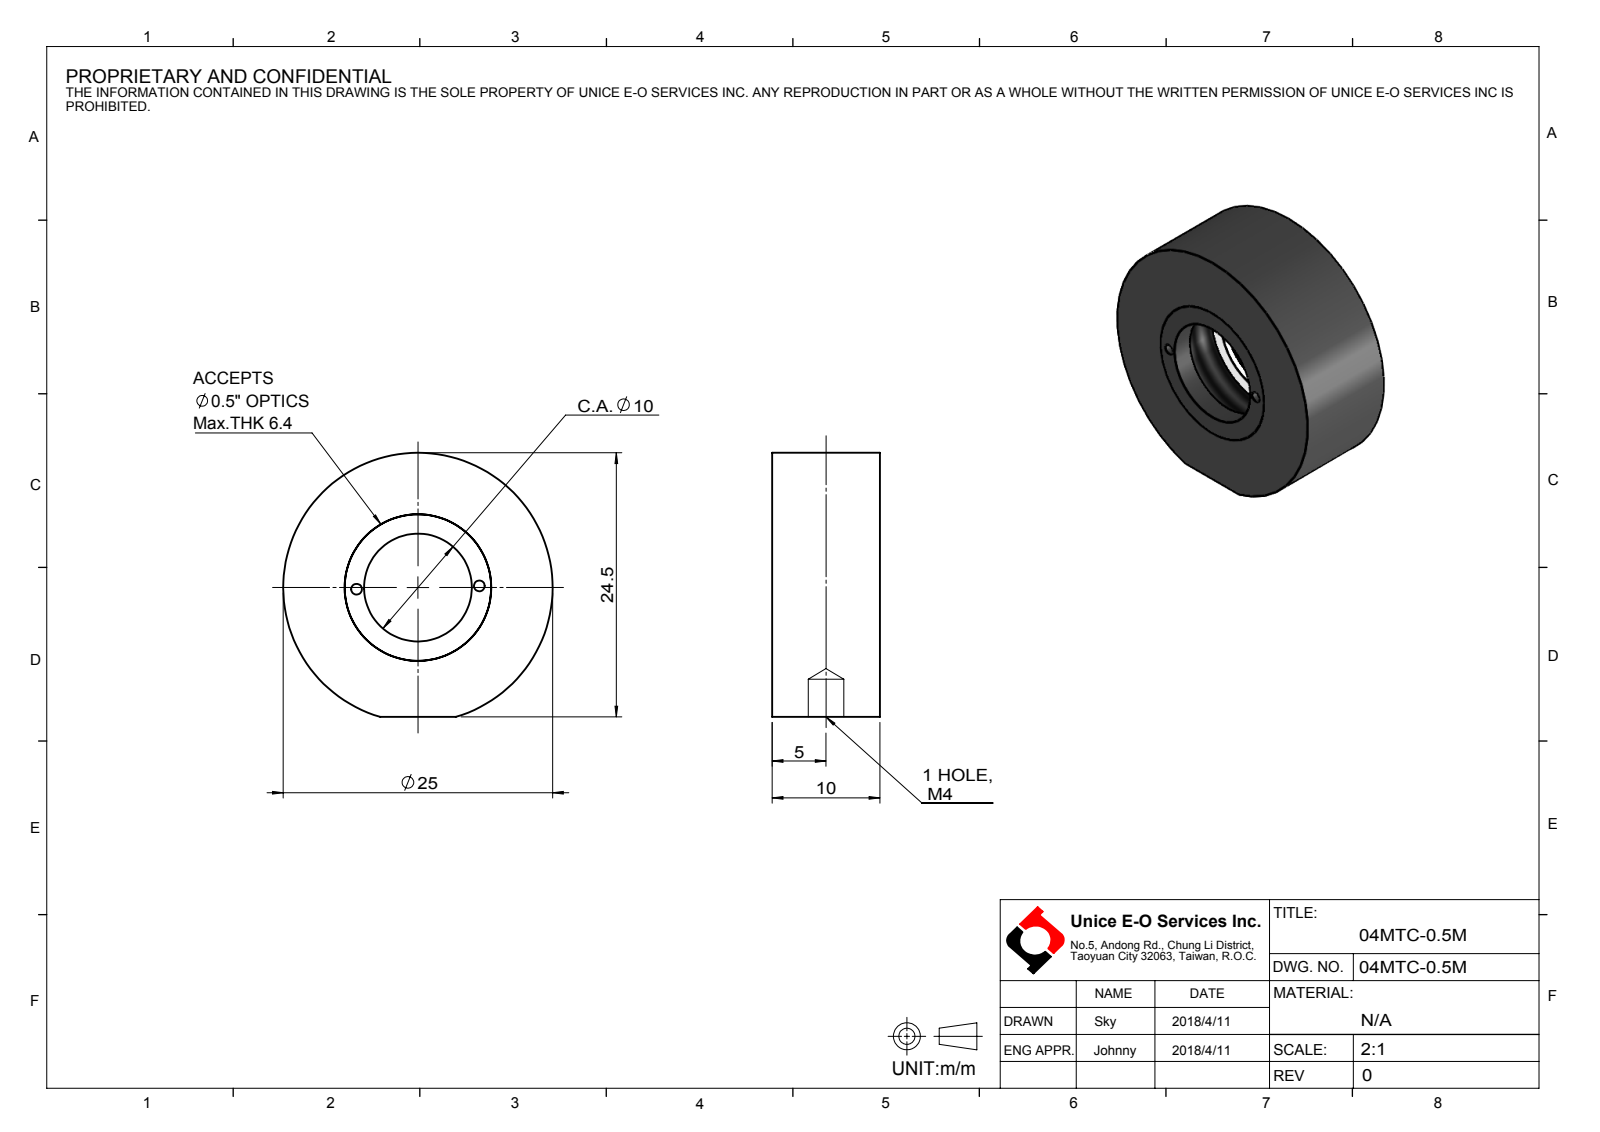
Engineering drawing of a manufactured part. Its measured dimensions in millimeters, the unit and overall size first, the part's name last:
Units: millimetres
Overall size (bounding box): 25 × 24.5 × 10
Round holes (diameter × count): ⌀1 ×2, ⌀3.3 ×1, ⌀10 ×1, ⌀13.6 ×1
Round bosses / shafts (diameter × count): ⌀25 ×1, ⌀12.5 ×1
Main face-to-face distances: 10, 1, 9, 8, 7, 2, 3.25, 3.85, 2.25, 2.85
Hole centre spacings: 5.69, 5.7, 11.39
Volume: 3 623 mm³ · Surface area: 2 480 mm²
Bodies: 3 solids, 31 faces (8 planar, 21 cylindrical, 2 other)
Part name (STEP PRODUCT): 04MTC-0.5M
STEP written by: SolidWorks 2016 (CONFIG_CONTROL_DESIGN)
